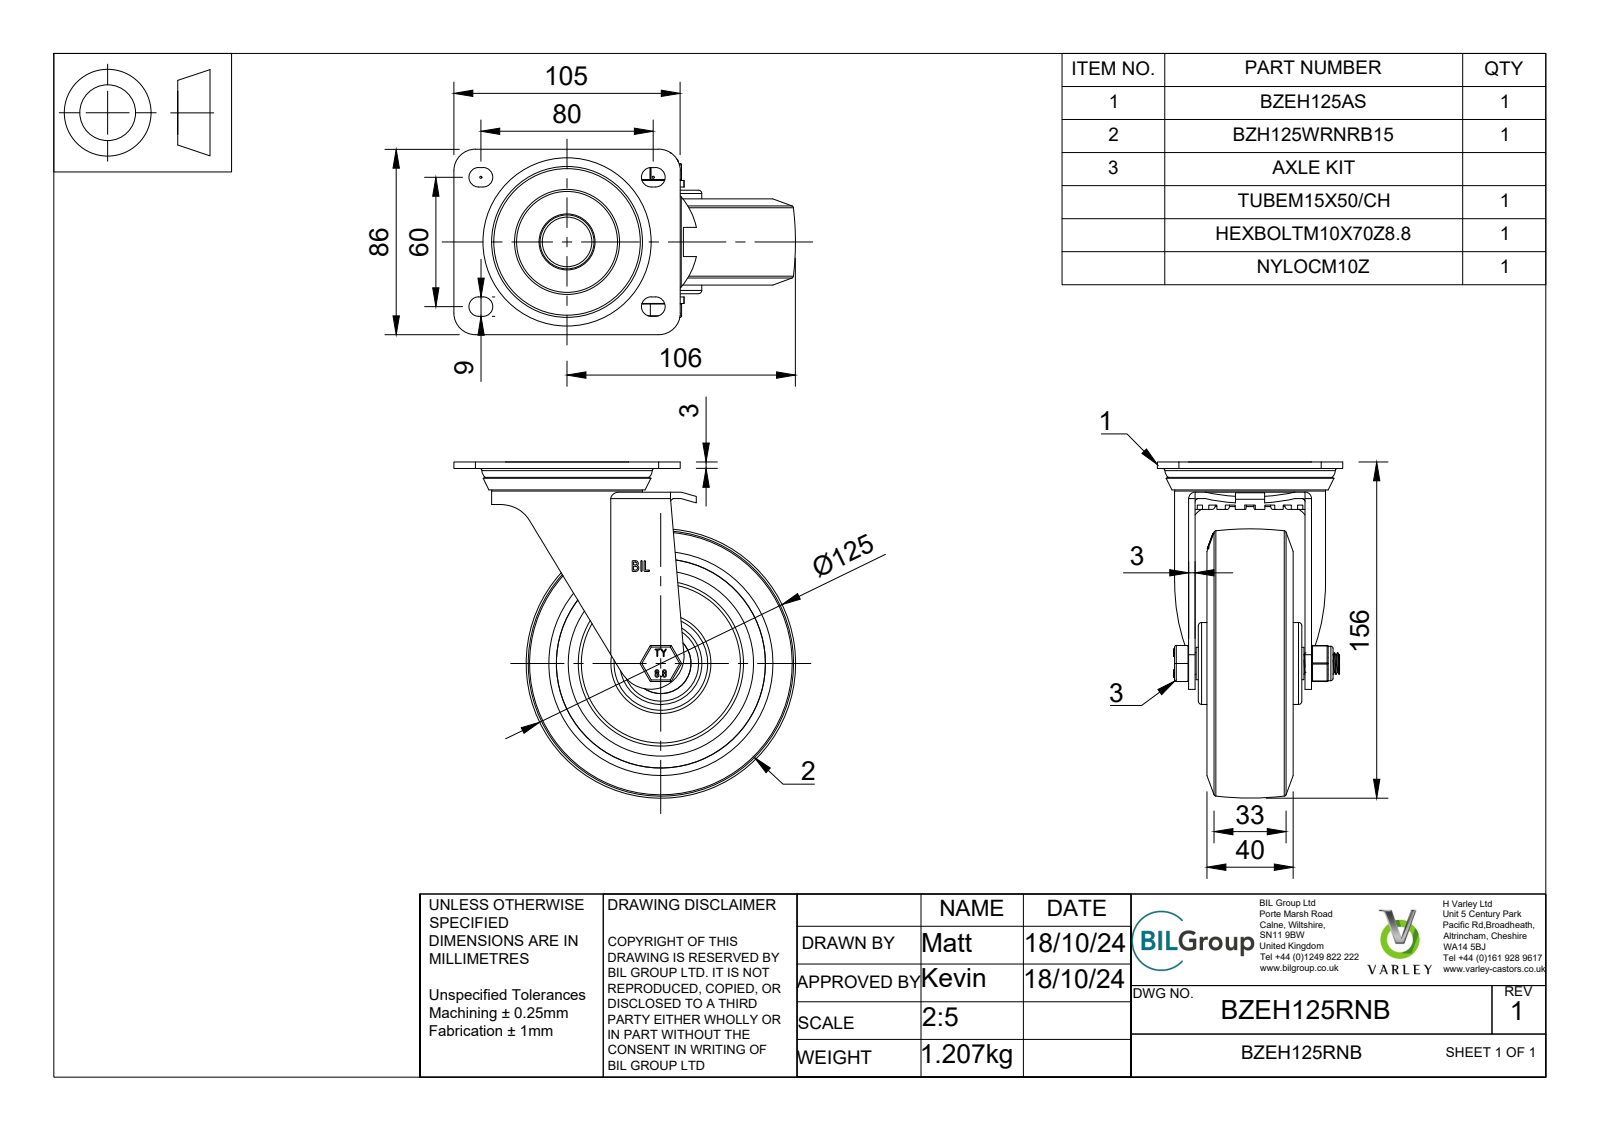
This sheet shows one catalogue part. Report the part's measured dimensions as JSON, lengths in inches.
{"part_name": "BZEH125RNB v4; BZEH125AS - 2 v1; ZINC PLATED, PRESSED STEEL TOP PLATE; ZINC PLATED, PRESSED STEEL TOP PLATE Geometry (+7 more)", "step_written_by": "Autodesk Translation Framework v13.20.0.188 (AUTOMOTIVE_DESIGN)", "units": "inches", "bodies": {"solids": 39, "faces": 633, "planar": 314, "cylindrical": 149, "other": 170}, "overall_size": [6.24, 6.142, 3.386], "volume_in3": 28.11, "surface_area_in2": 240, "round_holes": [[0.394, 1], [0.404, 1], [0.413, 1], [0.472, 1], [0.591, 1], [0.669, 1], [0.906, 1], [1.102, 1], [1.339, 1], [1.755, 1], [2.52, 1], [3.819, 1]], "round_bosses_or_shafts": [[0.157, 8], [0.63, 2], [2.756, 1], [2.126, 1], [1.496, 1], [1.098, 1], [0.984, 1], [0.896, 1]], "partial_cylinders_radius": [[0.02, 18], [0.177, 8], [0.03, 6], [0.059, 4], [0.394, 4], [0.118, 2], [1.244, 2], [0.369, 1]], "face_to_face_distances": [0.118, 0.591, 0.335, 0.217, 1.909, 2.126, 0.807, 0.925, 1.319, 0.984]}
